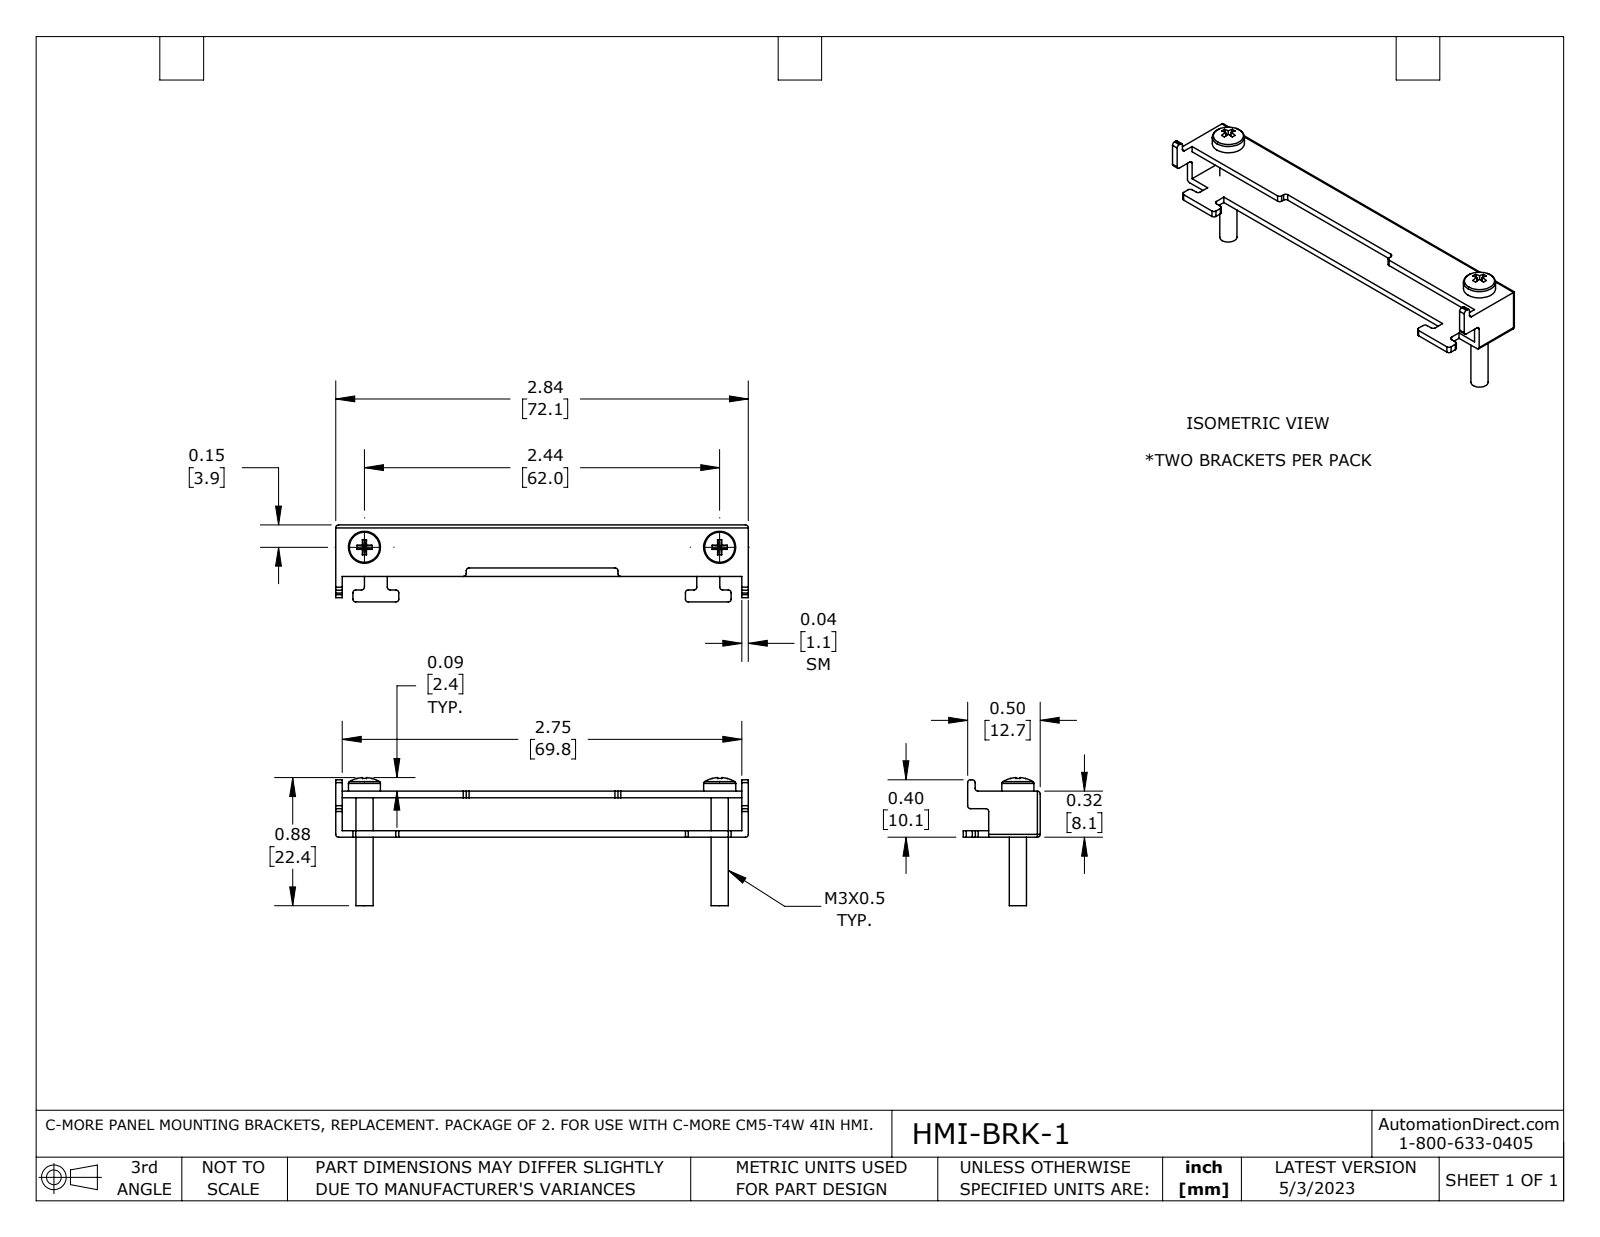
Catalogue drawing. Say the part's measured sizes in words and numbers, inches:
The part is named "HMI-BRK-1". Its 3-D file was written by "SolidWorks 2021 (AUTOMOTIVE_DESIGN)". It is 3 solids with 116 faces: 70 planar, 40 cylindrical and 6 other. Overall it measures 2.837 by 0.881 by 0.53 inches. Its volume is 0.149 cubic inches and its surface area 6.877 square inches. Round holes: 2 of diameter 0.098. Round bosses or shafts: 2 of diameter 0.22, 2 of diameter 0.118. Partial cylindrical surfaces (rounded edges, fillets, slot ends): 27 of radius 0.02. The main face-to-face distances are 0.045, 0.272, 0.317, 0.227, 0.354, 0.309, 2.792, 2.837, 2.747, 0.295. The hole center spacings are 2.442.
